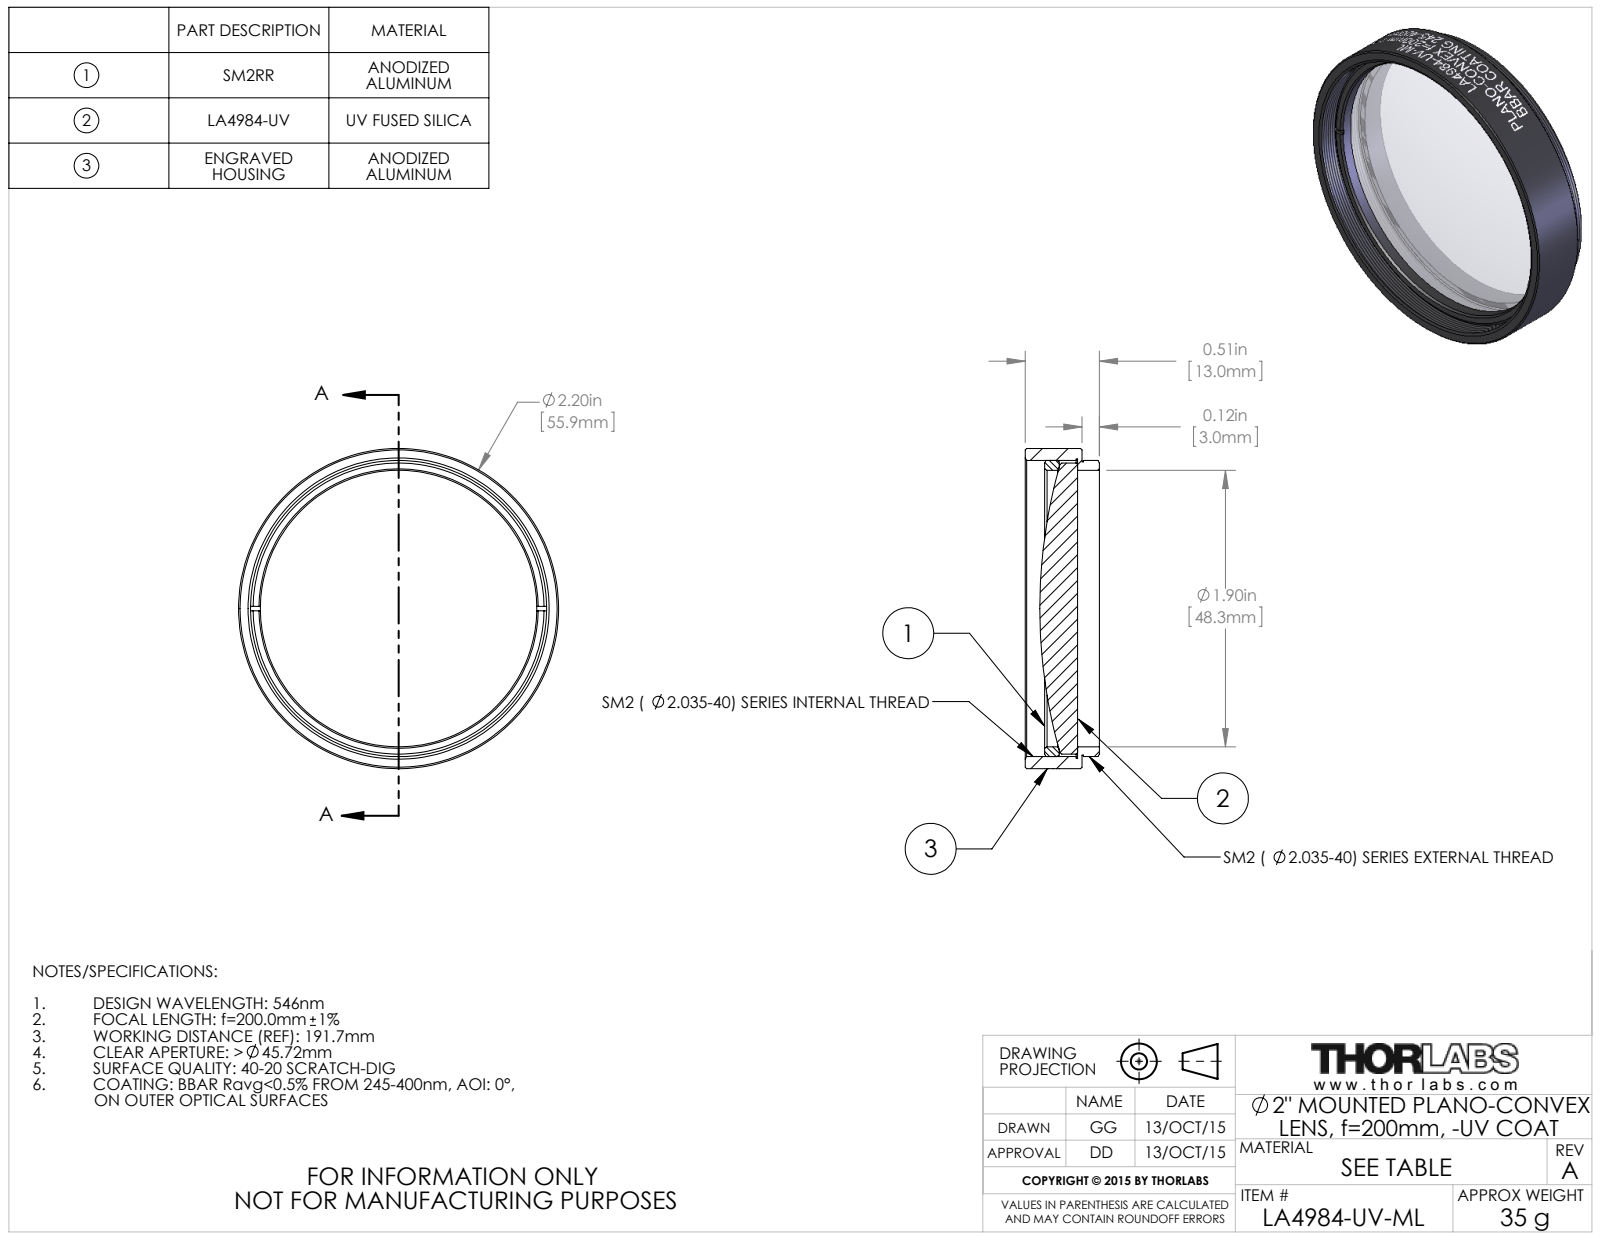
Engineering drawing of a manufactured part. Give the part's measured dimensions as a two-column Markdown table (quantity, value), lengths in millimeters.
| quantity | value |
| --- | --- |
| part name | TTN039464-E0W |
| STEP written by | SolidWorks 2014 (CONFIG_CONTROL_DESIGN) |
| units | millimeters |
| bodies | 3 solids, 151 faces (16 planar, 111 cylindrical, 24 other) |
| overall size | 55.88 × 55.88 × 12.95 |
| volume | 14 865 mm³ |
| surface area | 11 350 mm² |
| round holes (diameter × count) | 48.26 × 1, 52.2 × 1 |
| round bosses / shafts (diameter × count) | 55.88 × 1, 51.69 × 1, 51.18 × 1, 50.8 × 1 |
| main face-to-face distances | 0.76, 9.91, 9.15, 3.05, 3.81, 12.96, 7.05, 4, 3.24, 5.91 |
